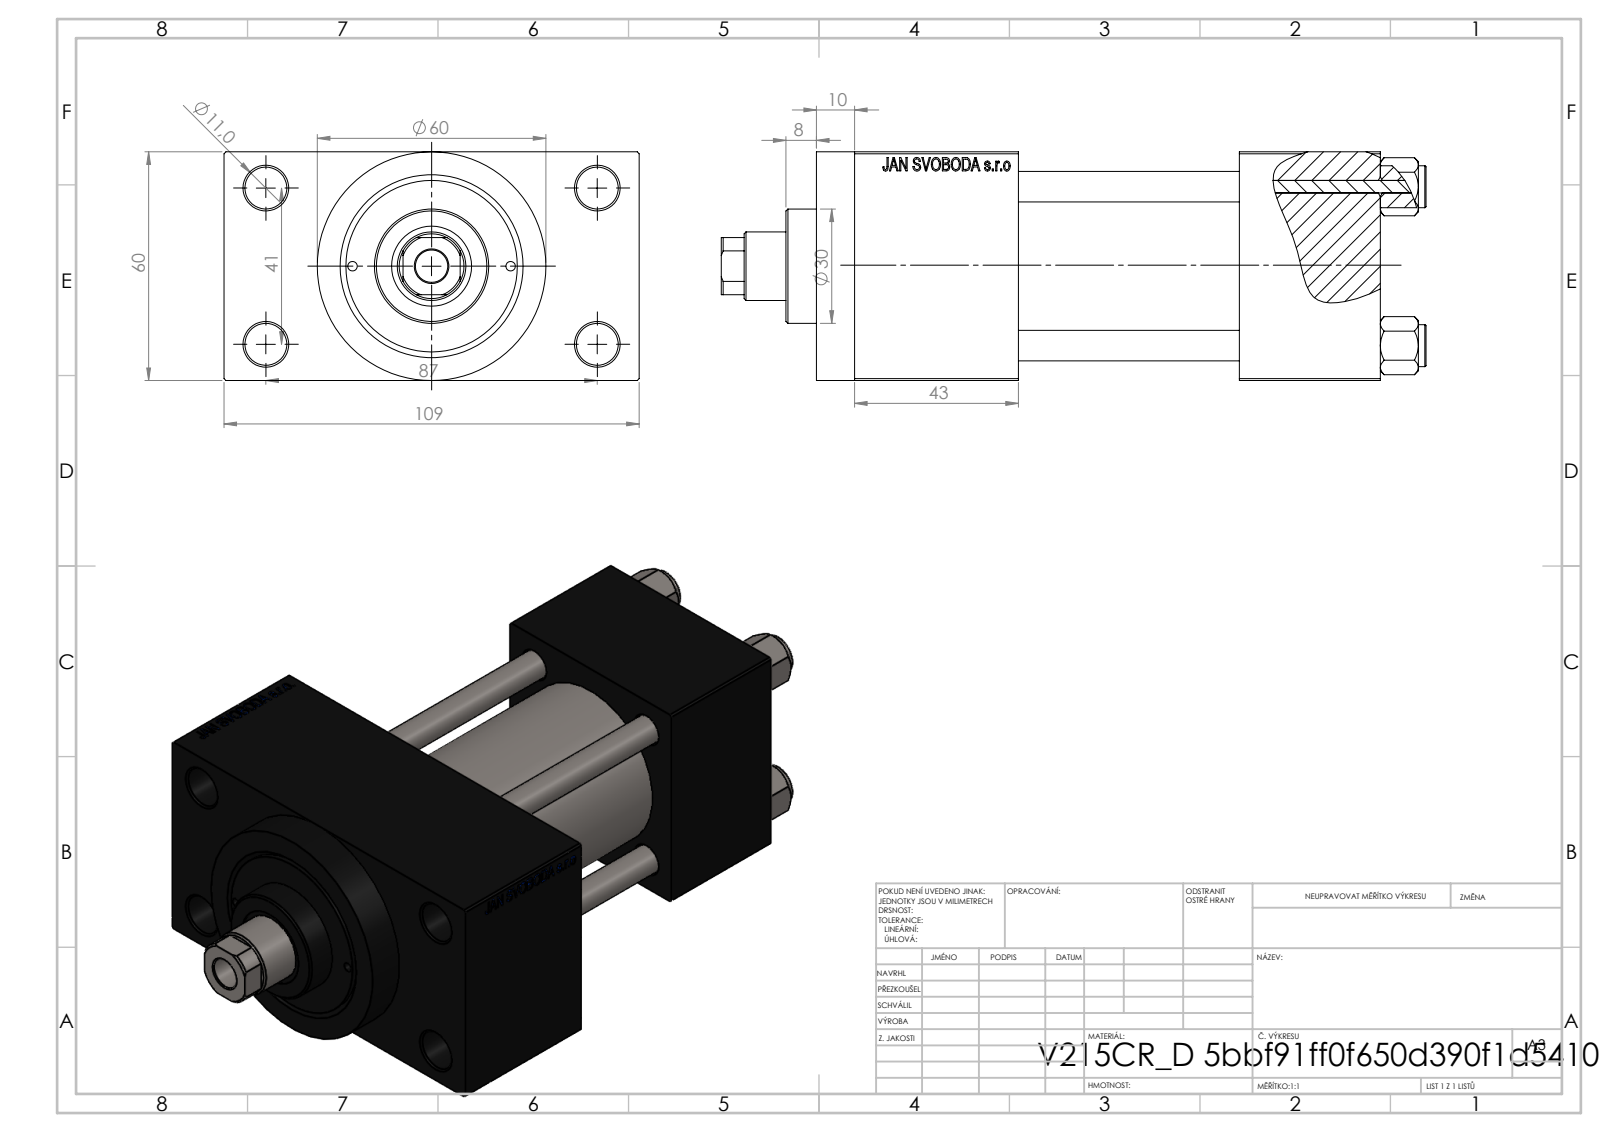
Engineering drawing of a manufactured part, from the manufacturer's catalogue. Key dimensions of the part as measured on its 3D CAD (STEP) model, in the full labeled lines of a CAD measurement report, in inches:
Part name (STEP PRODUCT): V215CR_D_Body; NUT_M5_D; V215CR_D_TYCINKA; V215CR_VCP_D (+1 more)
STEP written by: SolidWorks 2019 (CONFIG_CONTROL_DESIGN)
Units: inches
Bodies: 11 solids, 1112 faces (500 planar, 92 cylindrical, 520 other)
Overall size (bounding box): 7.283 × 4.291 × 2.362
Volume: 31.26 in³ · Surface area: 189.9 in²
Round holes (diameter × count): ⌀0.315 ×4, ⌀0.433 ×4, ⌀0.098 ×2, ⌀0.276 ×2, ⌀0.656 ×2, ⌀0.945 ×2, ⌀0.335 ×1, ⌀0.709 ×1, ⌀0.827 ×1, ⌀1.22 ×1, ⌀1.575 ×1, ⌀1.772 ×1
Round bosses / shafts (diameter × count): ⌀0.433 ×4, ⌀2.362 ×1, ⌀1.811 ×1, ⌀1.181 ×1
Partial cylindrical surfaces — rounded edges, fillets, slot ends (radius × count): R0.335 ×1
Main face-to-face distances: 2.362, 2.283, 0.965, 3.327, 1.457, 3.74, 5.433, 3.976, 1.693, 4.124
Hole centre spacings: 0.821, 0.892, 1.161, 1.206, 1.642, 1.832, 1.856, 1.893
